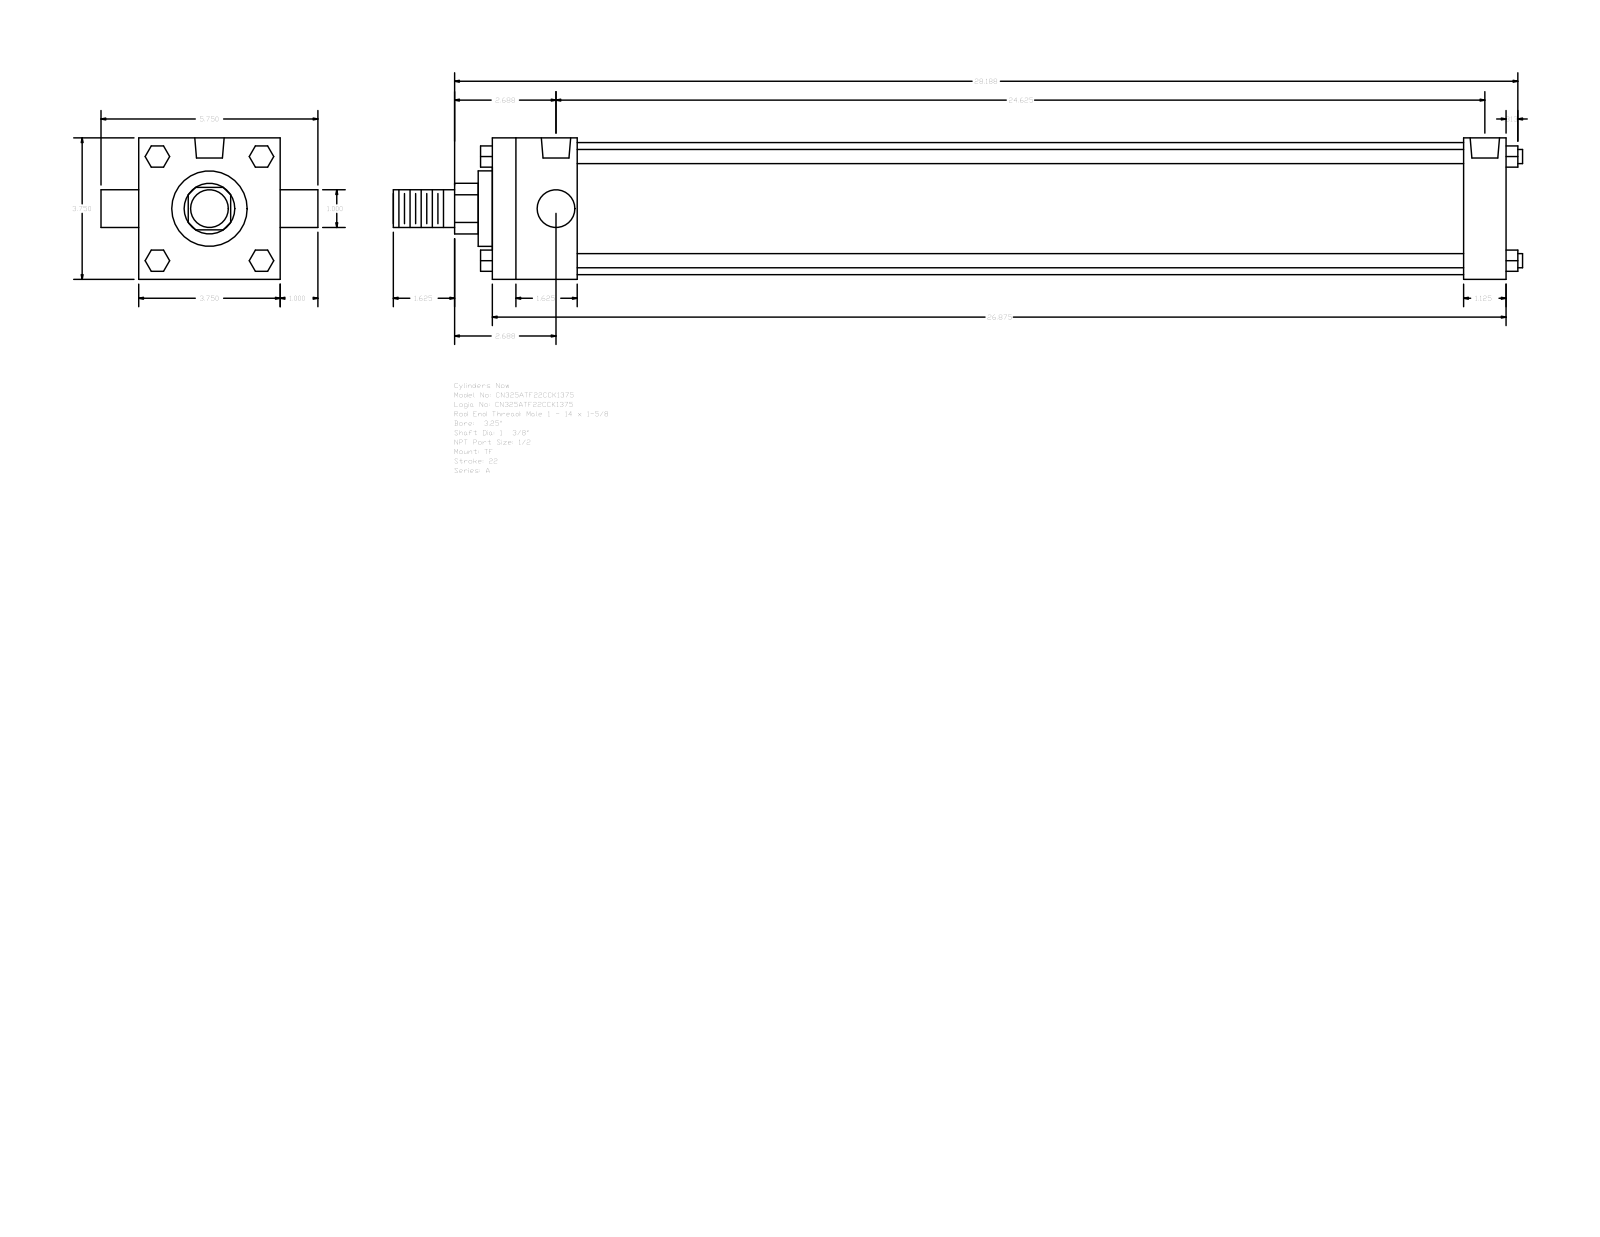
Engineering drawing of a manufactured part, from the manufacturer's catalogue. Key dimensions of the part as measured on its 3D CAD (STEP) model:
Part name (STEP PRODUCT): A_TF__0325_1.375
STEP written by: GSSL Pune (CONFIG_CONTROL_DESIGN)
Units: millimetres
Bodies: 0 solids, 120 faces (92 planar, 28 cylindrical, 0 other)
Overall size (bounding box): 760.41 × 146.05 × 95.25
Round holes (diameter × count): ⌀8.73 ×3, ⌀19.77 ×2
Round bosses / shafts (diameter × count): ⌀9.53 ×4, ⌀25.4 ×2, ⌀88.9 ×1, ⌀50.8 ×1, ⌀34.92 ×1
Partial cylindrical surfaces — rounded edges, fillets, slot ends (radius × count): R17.06 ×1
Main face-to-face distances: 95.24, 682.62, 57.15, 654.05, 596.9, 625.47, 28.57, 66.67, 9.52, 663.57
Hole centre spacings: 3.18, 622.3, 619.12, 625.48
